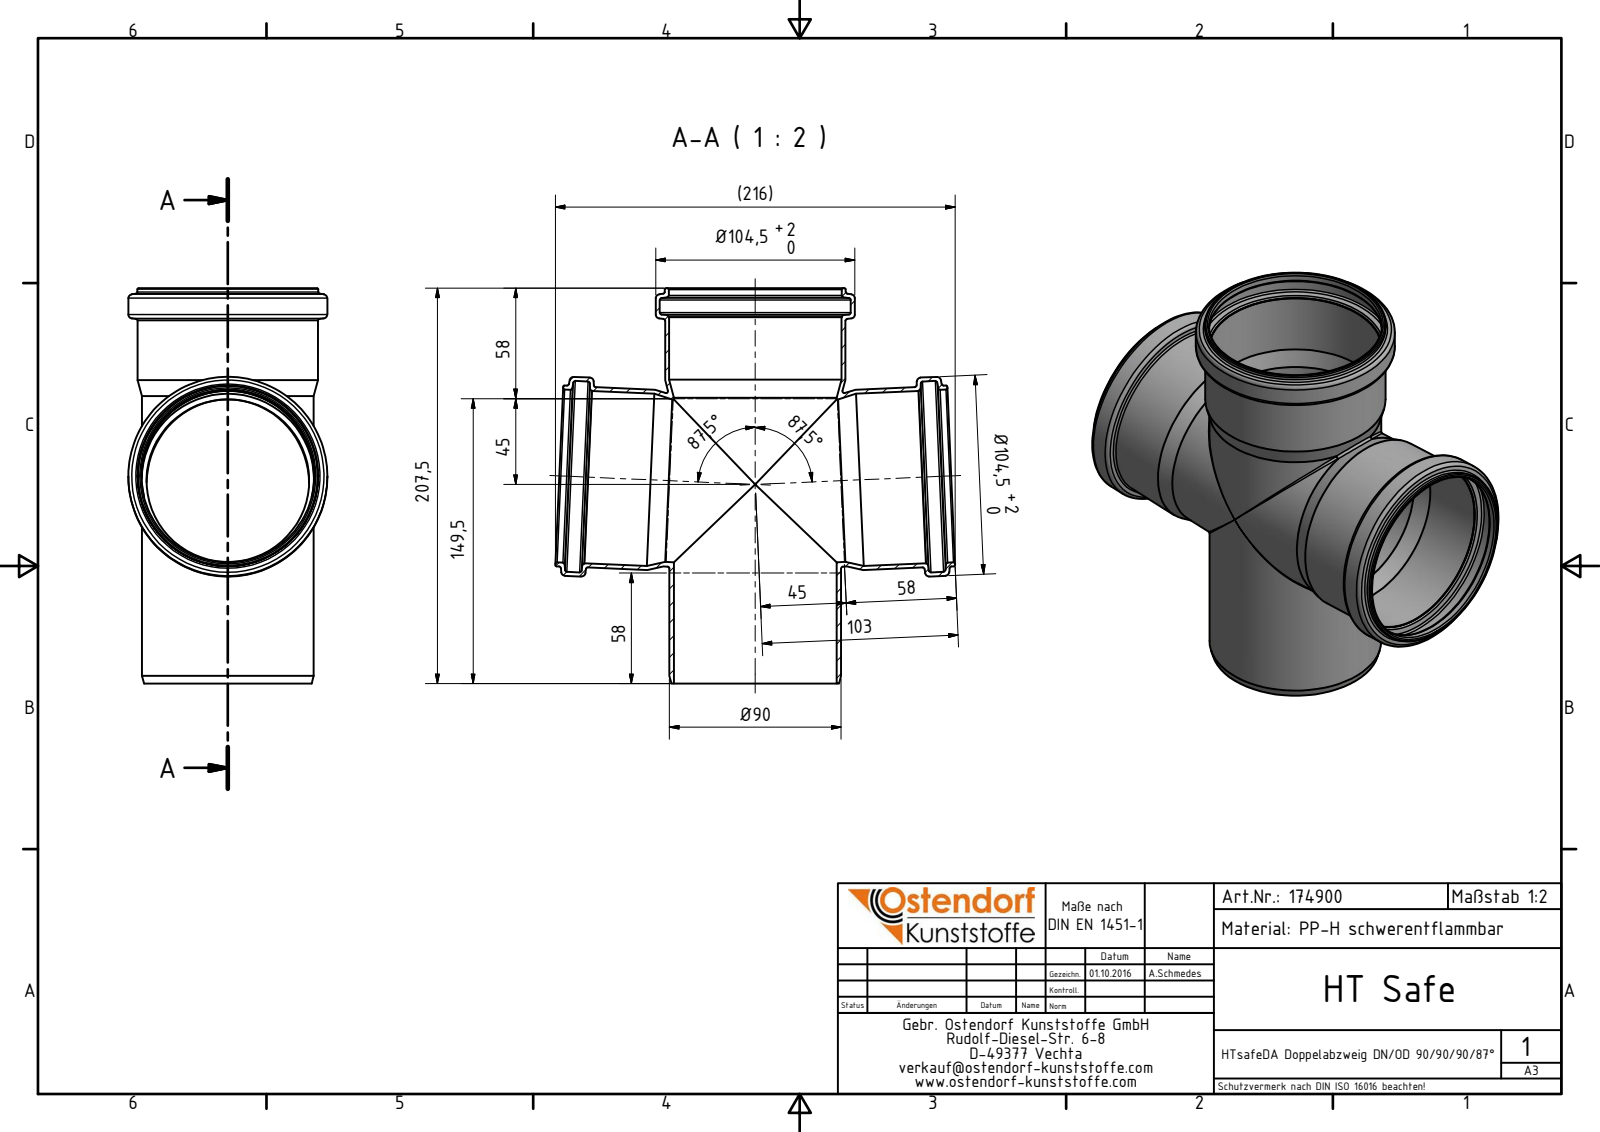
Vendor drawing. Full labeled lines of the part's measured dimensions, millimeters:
Part name (STEP PRODUCT): 174900 HTsafeDA DN_OD 90_90_90_87°
STEP written by: Autodesk Inventor 2016 (AUTOMOTIVE_DESIGN)
Units: millimetres
Bodies: 1 solid, 94 faces (7 planar, 30 cylindrical, 57 other)
Overall size (bounding box): 209.91 × 207.5 × 104.5
Volume: 208 144 mm³ · Surface area: 188 126 mm²
Round holes (diameter × count): ⌀85.4 ×3, ⌀90.5 ×3, ⌀90.8 ×3, ⌀100.3 ×3
Round bosses / shafts (diameter × count): ⌀104.5 ×3, ⌀95 ×3, ⌀94.7 ×3, ⌀90.2 ×3
Main face-to-face distances: 207.5, 15.21, 192.29
